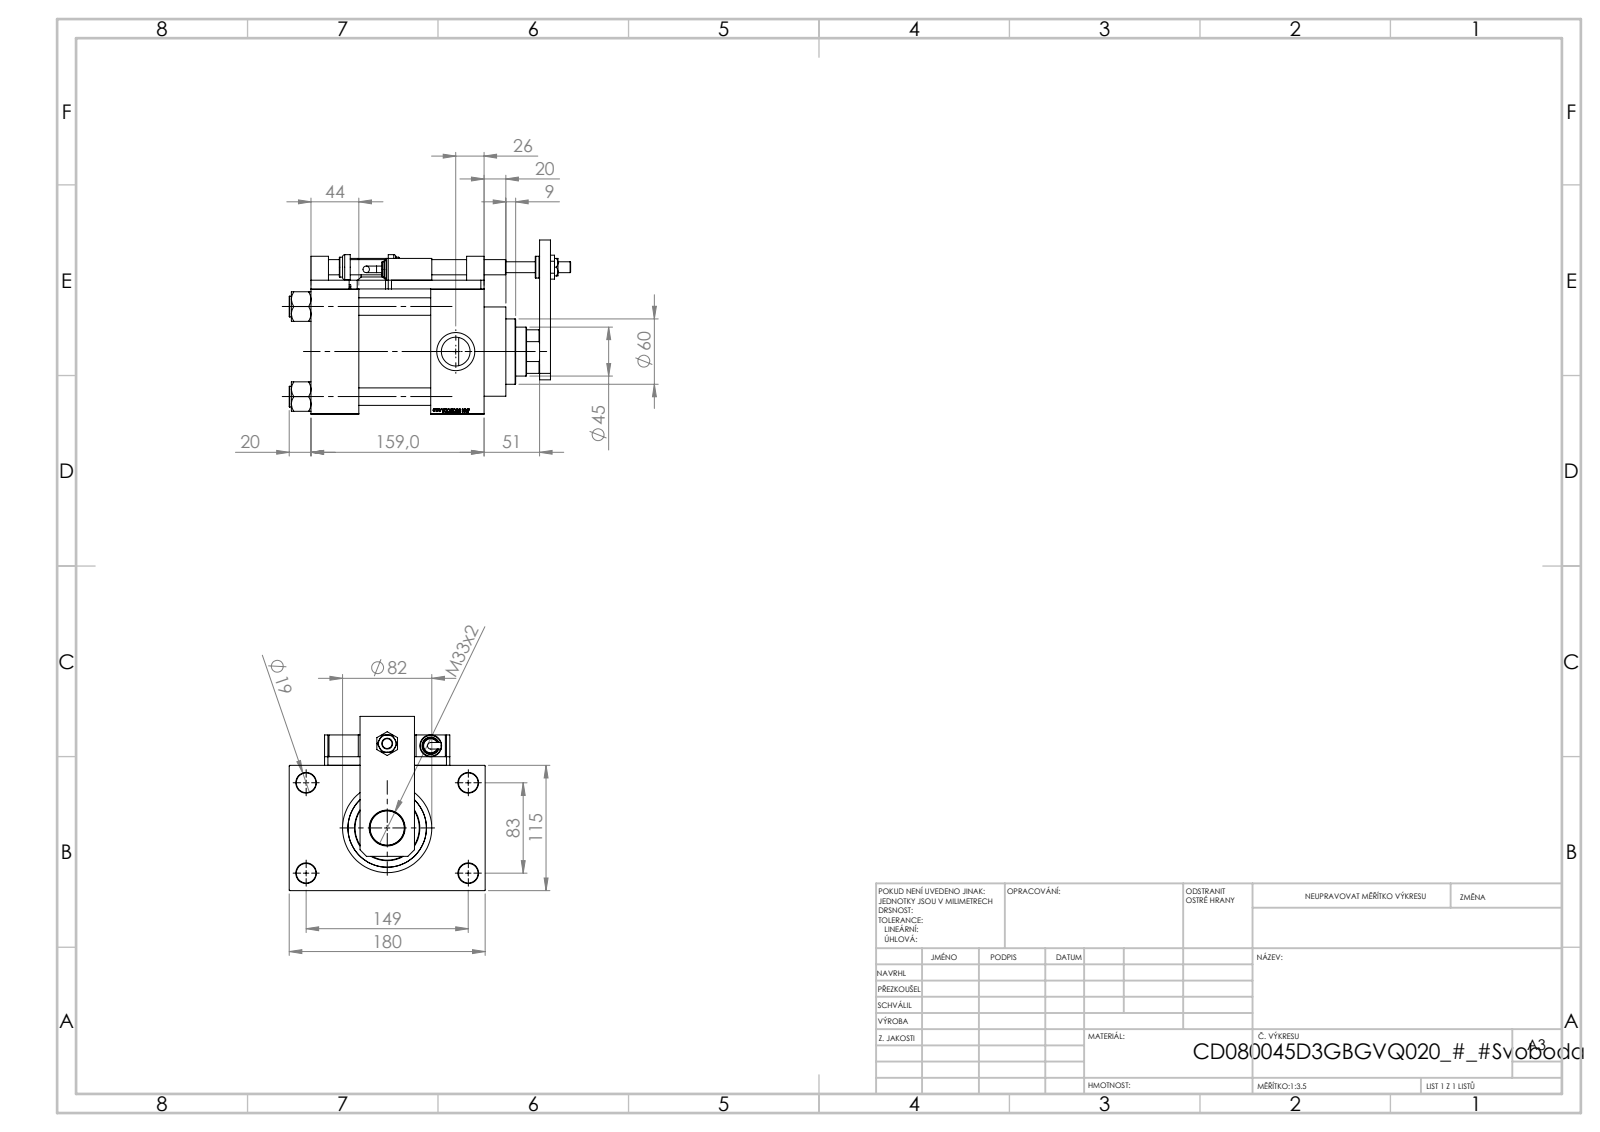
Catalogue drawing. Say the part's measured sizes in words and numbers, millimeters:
The part is named "V215CD_D_TYCINKA; V215CD_D_Body; V215CD_SWITCH_Q_TYC; V215CD_SWITCH_Q_PODLOZKA_FRONT (+8 more)". Its 3-D file was written by "SolidWorks 2019 (CONFIG_CONTROL_DESIGN)". It is 26 solids with 1480 faces: 714 planar, 167 cylindrical and 599 other. Overall it measures 258.5 by 180 by 160 millimeters. Its volume is 2 282 000 cubic millimeters and its surface area 399 868 square millimeters. Round holes: 4 of diameter 8.5, 4 of diameter 13.5, 4 of diameter 16, 4 of diameter 18, 4 of diameter 26.44, 4 of diameter 35, 3 of diameter 7, 1 of diameter 10, 1 of diameter 14, 1 of diameter 31.5, 1 of diameter 33, 1 of diameter 45. Round bosses or shafts: 4 of diameter 19, 3 of diameter 20, 2 of diameter 16, 2 of diameter 14, 2 of diameter 6, 1 of diameter 86, 1 of diameter 82, 1 of diameter 60. Partial cylindrical surfaces (rounded edges, fillets, slot ends): 4 of radius 7.5, 1 of radius 22. The main face-to-face distances are 115, 110, 8, 66, 49, 44, 123, 159, 32.5, 20. The hole center spacings are 33.15, 58.48, 82.7, 85.28, 89.24, 115.85, 142.43, 21.26.
